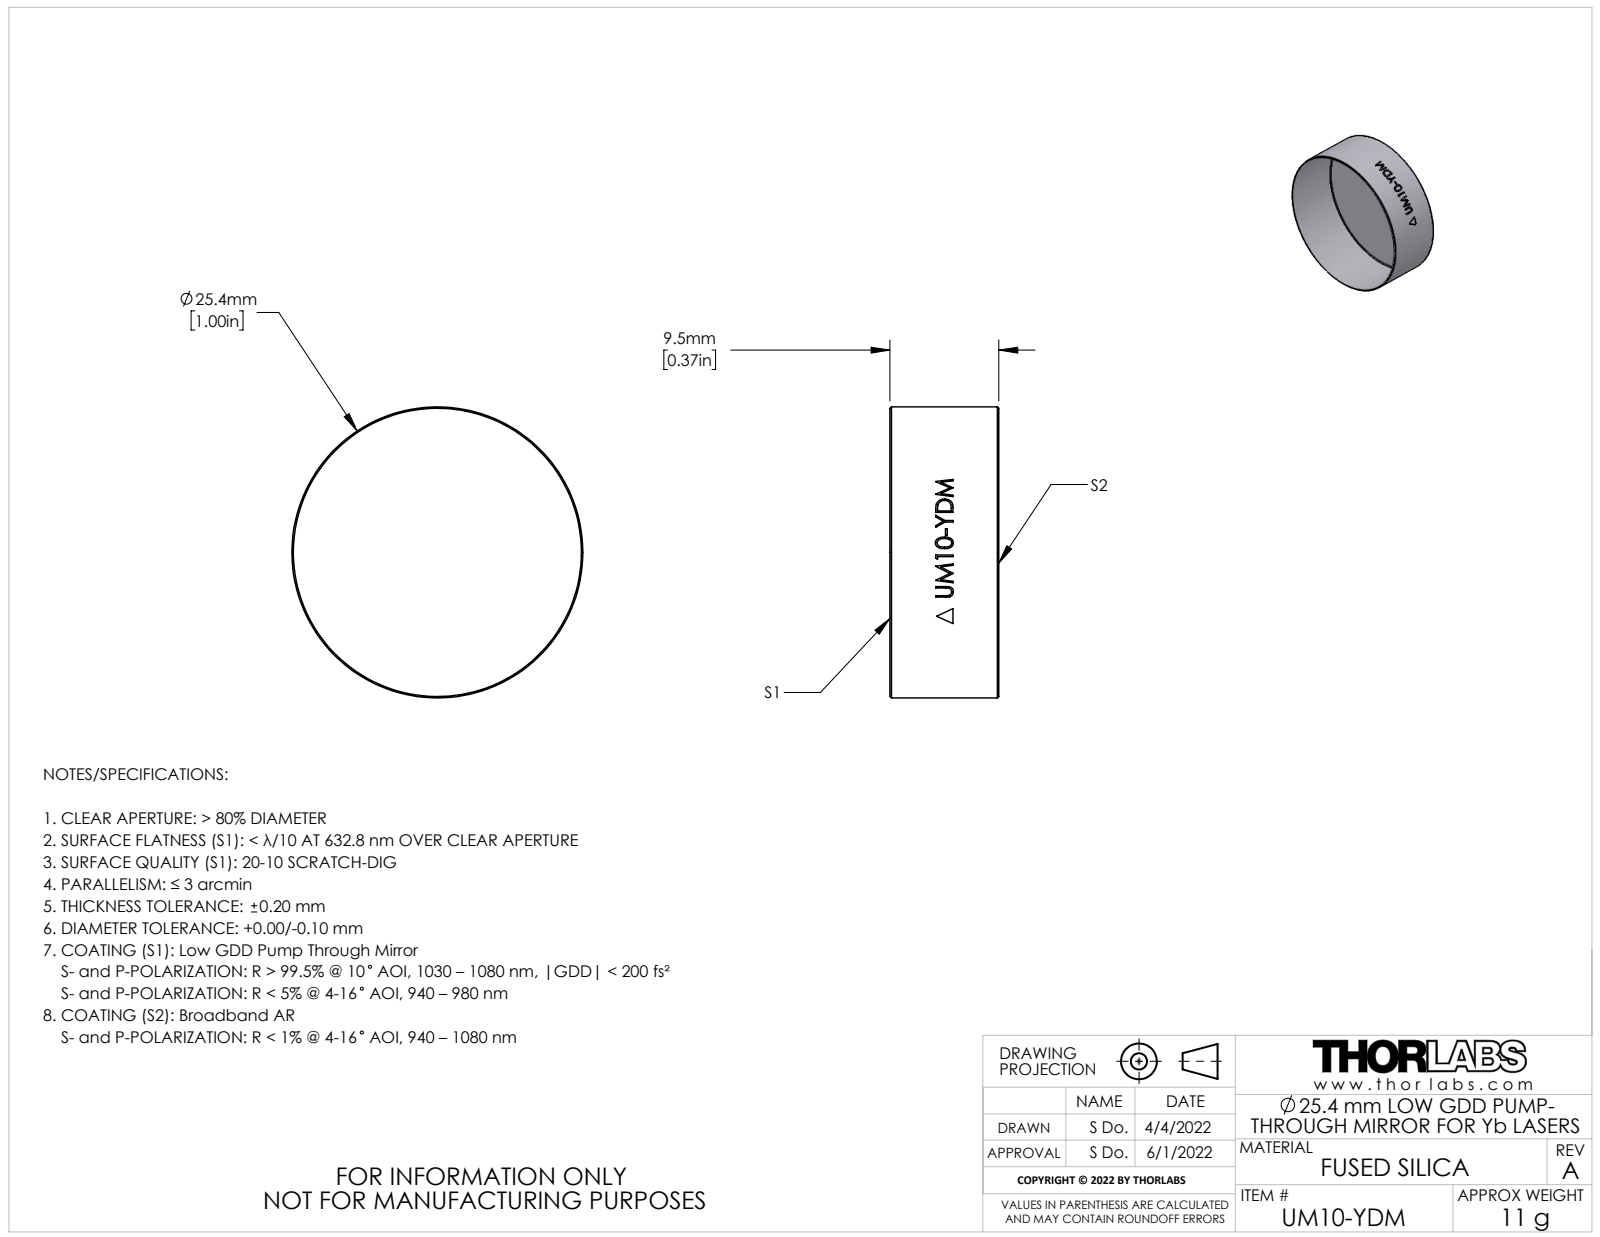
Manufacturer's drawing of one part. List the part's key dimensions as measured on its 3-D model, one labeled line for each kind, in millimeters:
Part name (STEP PRODUCT): TTN283369-E0W
STEP written by: SolidWorks 2018 (AUTOMOTIVE_DESIGN)
Units: millimetres
Bodies: 1 solid, 23 faces (2 planar, 17 cylindrical, 4 other)
Overall size (bounding box): 25.4 × 25.4 × 9.5
Volume: 4 812 mm³ · Surface area: 1 760 mm²
Round holes (diameter × count): ⌀25.15 ×1
Round bosses / shafts (diameter × count): ⌀25.4 ×1
Main face-to-face distances: 9.5
